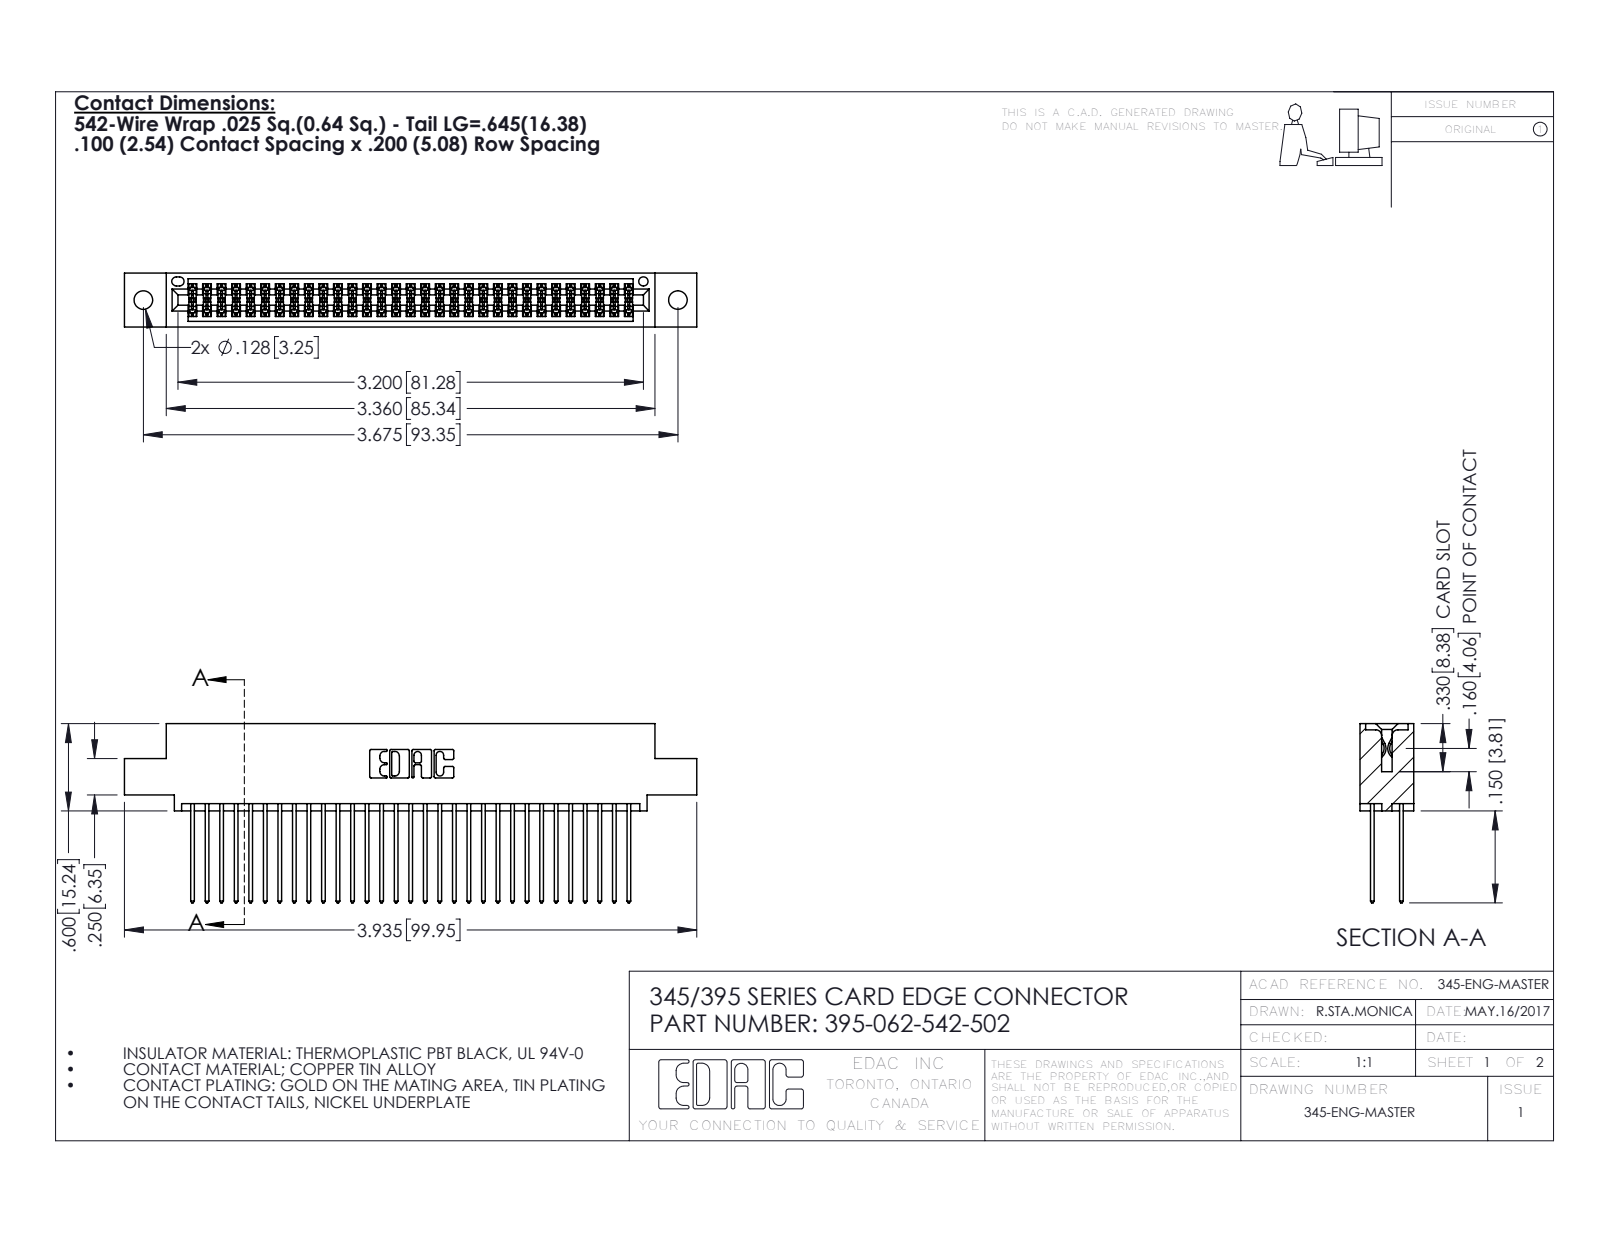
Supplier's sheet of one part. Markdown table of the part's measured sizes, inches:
| quantity | value |
| --- | --- |
| part name | 395-062-542-502; 345-292-001_345-293-142; 345 Part_0.110 Offset - 0.128 Dia |
| STEP written by | SolidWorks 2016 (CONFIG_CONTROL_DESIGN) |
| units | inches |
| bodies | 63 solids, 3230 faces (2130 planar, 1100 cylindrical, 0 other) |
| overall size | 3.935 × 1.232 × 0.37 |
| volume | 0.597 in³ |
| surface area | 23.91 in² |
| round holes (diameter × count) | 0.128 × 2, 0.064 × 1 |
| partial cylindrical surfaces (radius × count) | 0.006 × 93, 0.01 × 62, 0.01 × 22, 0.007 × 6, 0.031 × 6, 0.026 × 3, 0.014 × 2, 0.019 × 2 |
| main face-to-face distances | 0.298, 0.072, 0.2, 0.098, 0.272, 0.025, 0.37, 0.225, 0.175, 0.149 |
| hole center spacings | 0.27, 3.44, 3.675 |
